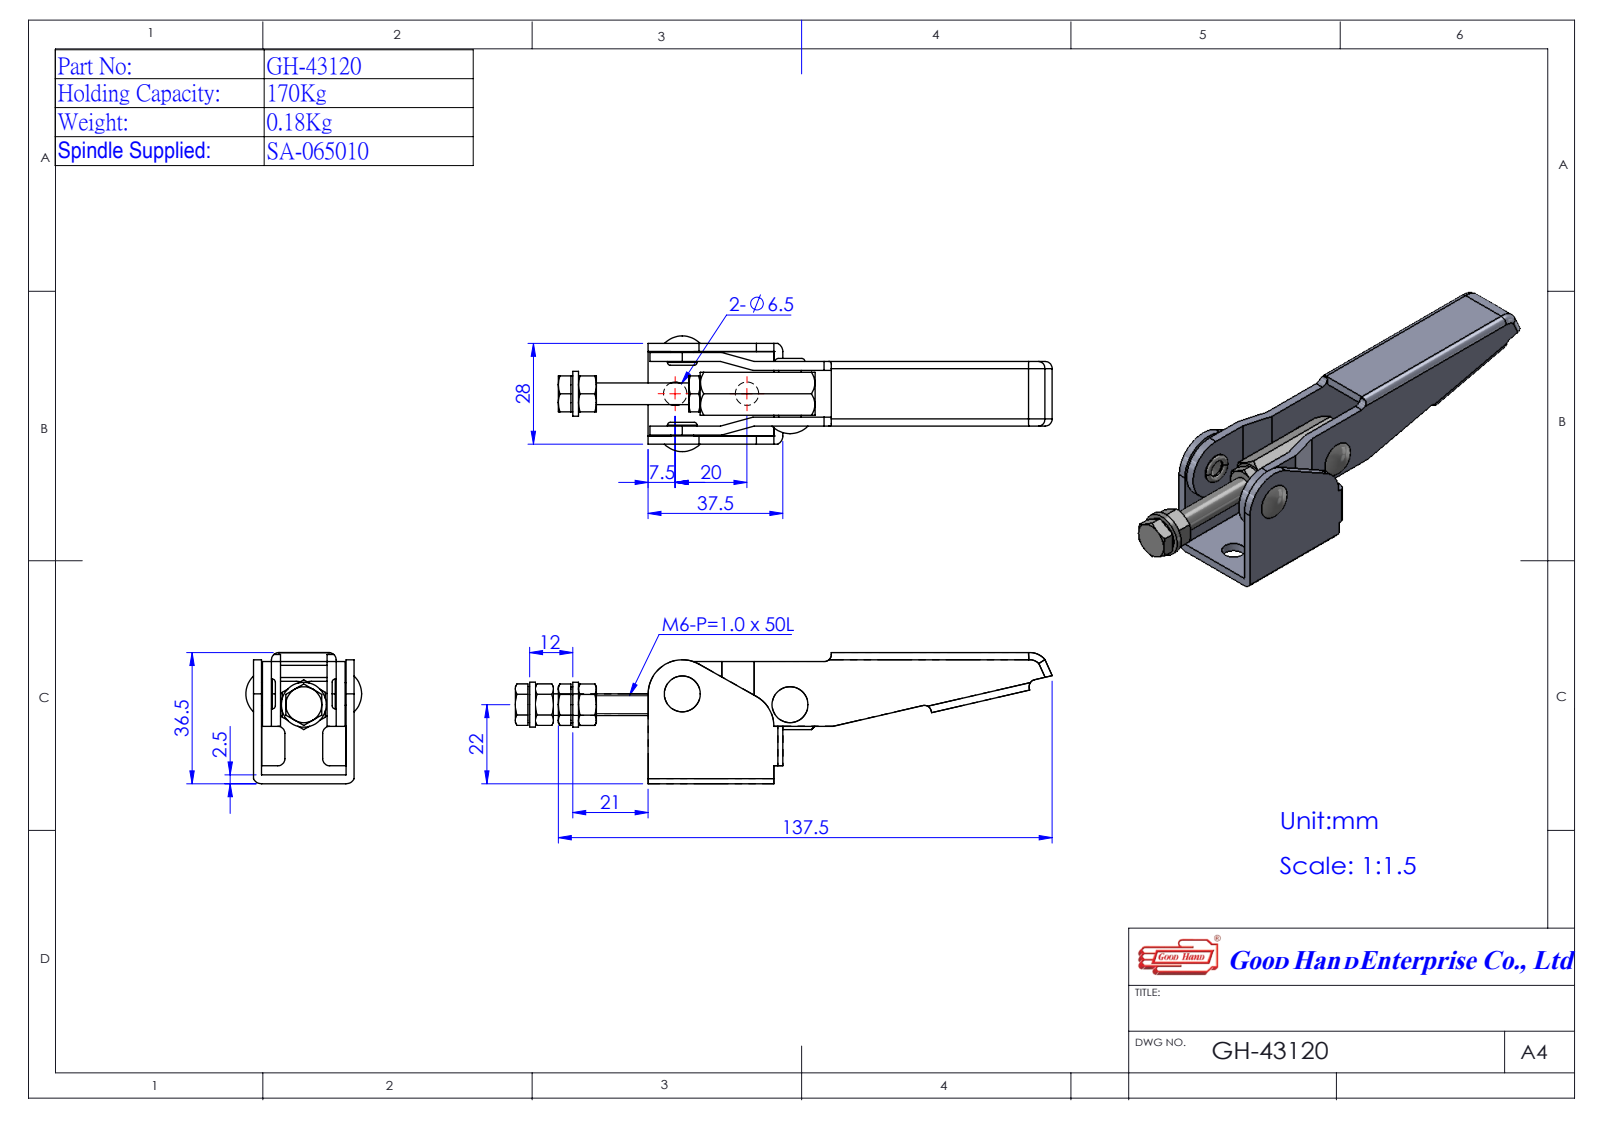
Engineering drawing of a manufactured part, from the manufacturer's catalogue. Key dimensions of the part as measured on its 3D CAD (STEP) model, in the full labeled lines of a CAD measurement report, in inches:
Part name (STEP PRODUCT): GH-43120(簡化); Continuous Thread Hexagon Head Bolt_A_JIS-4^GH-43120(簡化); Group3^GH-43120(簡化); Group2^GH-43120(簡化) (+1 more)
STEP written by: SolidWorks 2016 (AUTOMOTIVE_DESIGN)
Units: inches
Bodies: 4 solids, 219 faces (93 planar, 76 cylindrical, 50 other)
Overall size (bounding box): 5.374 × 1.437 × 1.268
Volume: 1.501 in³ · Surface area: 32.55 in²
Round holes (diameter × count): ⌀0.197 ×3, ⌀0.26 ×2, ⌀0.236 ×1, ⌀0.276 ×1
Round bosses / shafts (diameter × count): ⌀0.394 ×1, ⌀0.327 ×1, ⌀0.248 ×1
Partial cylindrical surfaces — rounded edges, fillets, slot ends (radius × count): R0.079 ×17, R0.099 ×4, R0.374 ×2, R0.138 ×1, R0.217 ×1, R0.354 ×1
Main face-to-face distances: 0.098, 0.807, 0.197, 0.709, 0.906, 0.61, 0.108, 0.207, 0.089, 0.719
Hole centre spacings: 0.787, 1.187
